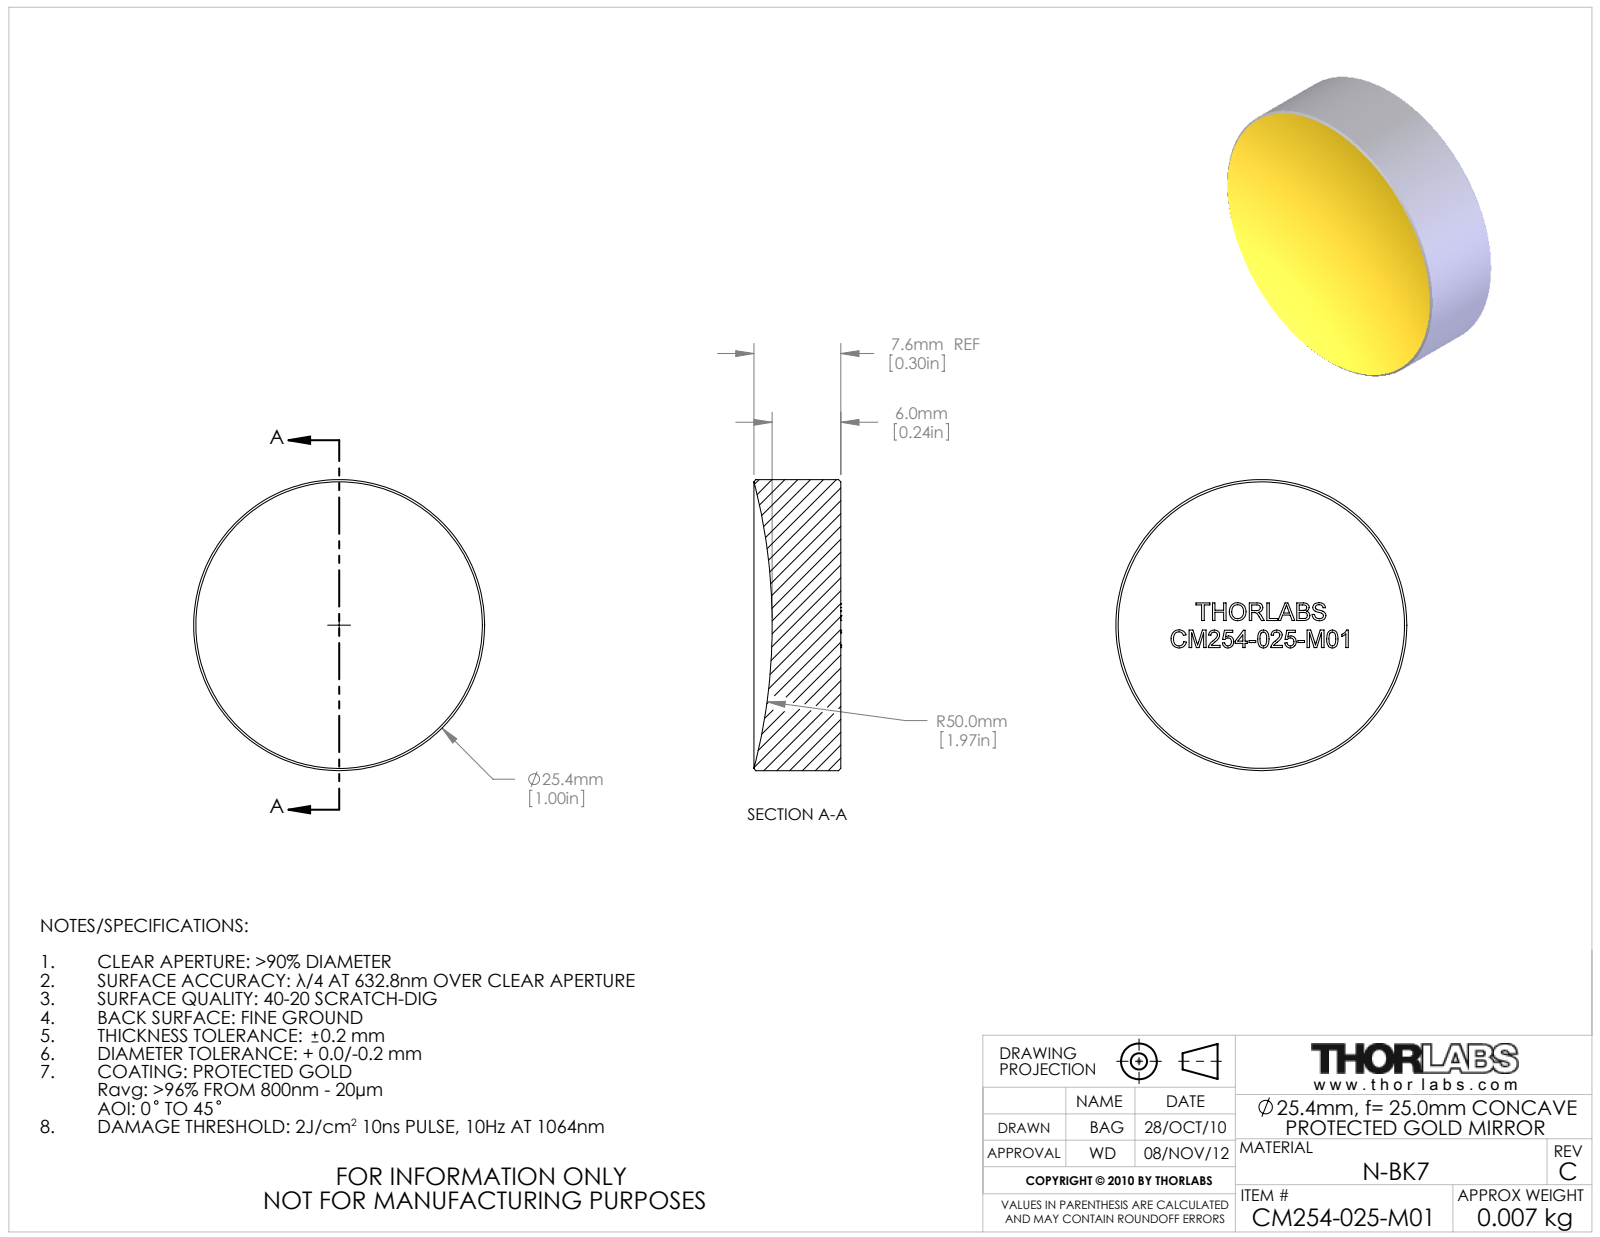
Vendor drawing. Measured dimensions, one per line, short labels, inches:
name: 17582-E0W
written by: SolidWorks 2009 (AUTOMOTIVE_DESIGN)
unit: in
bodies: 1 solid, 286 faces (166 planar, 2 cylindrical, 118 other)
size: 1 × 1 × 0.299
volume: 0.211 in³; area: 2.495 in²
bosses: 1× ⌀1
face distances: 0.061, 0.076, 0.093, 0.405, 0.037, 0.094, 0.05, 0.043, 0.058, 0.038
